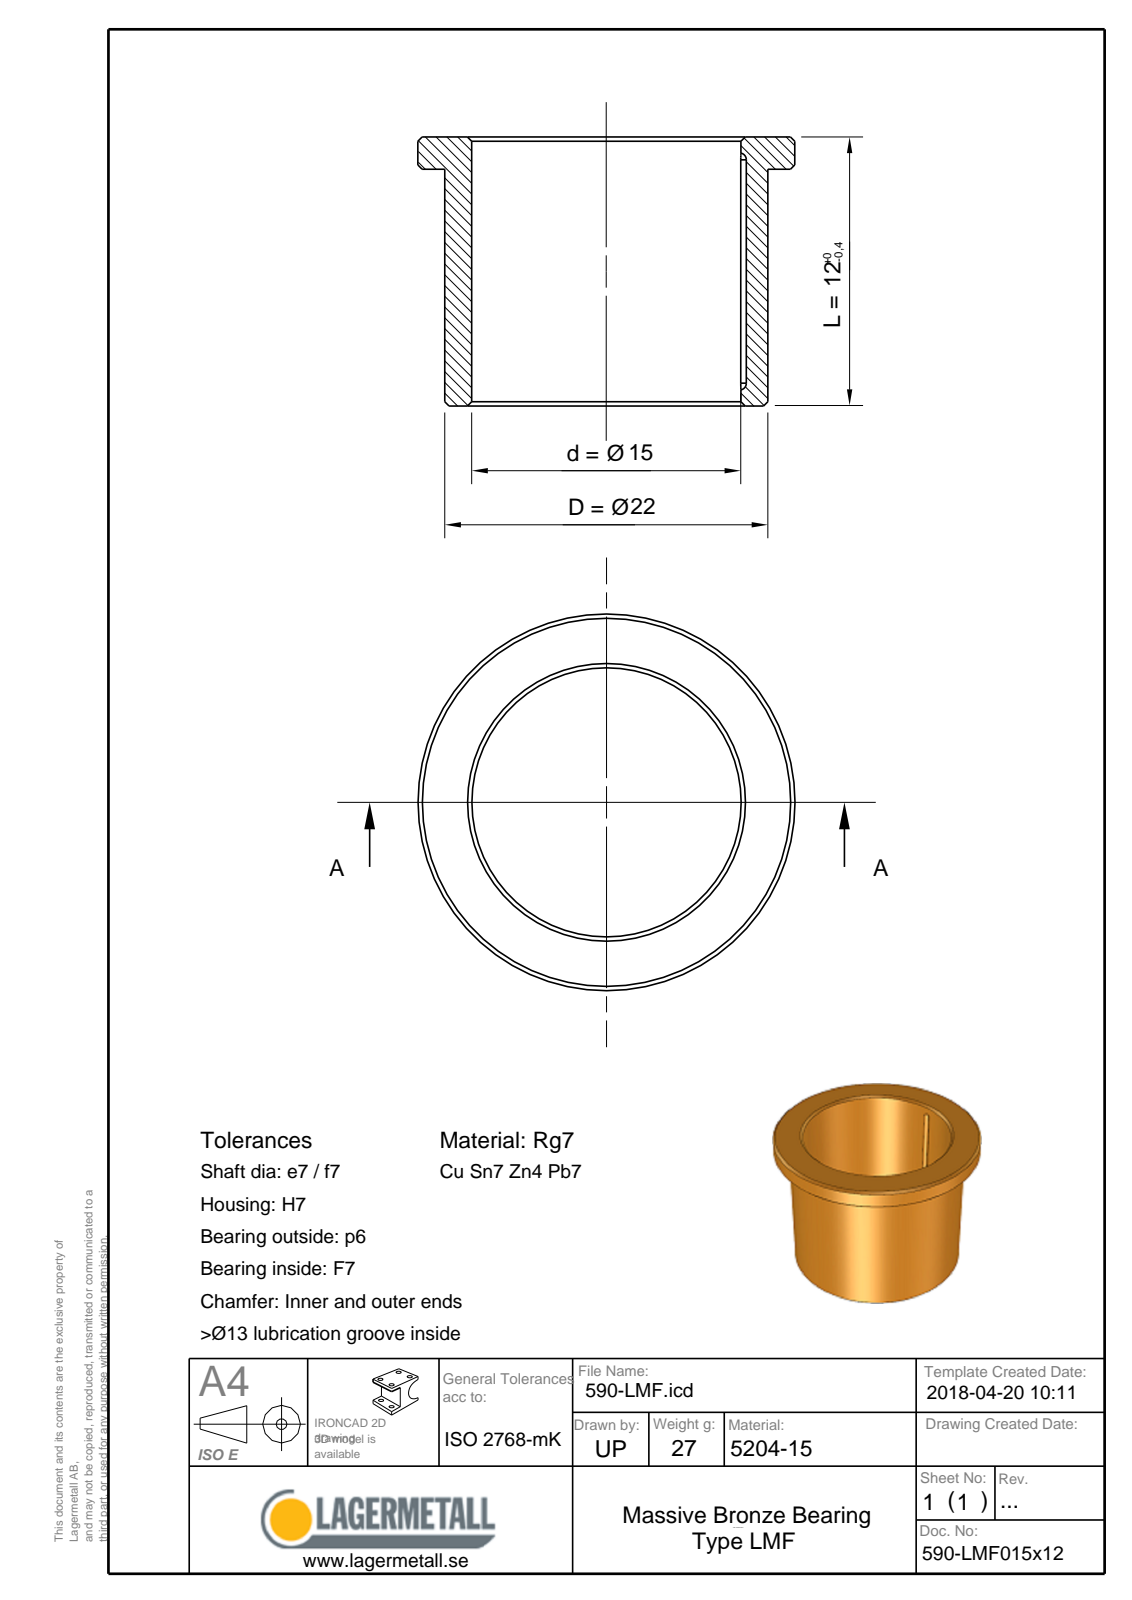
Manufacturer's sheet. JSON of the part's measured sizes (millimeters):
{"part_name": "590-LMF015x12", "step_written_by": "Spatial InterOp 3D (CONFIG_CONTROL_DESIGN)", "units": "millimeters", "bodies": {"solids": 1, "faces": 18, "planar": 5, "cylindrical": 6, "other": 7}, "overall_size": [28, 28, 12], "volume_mm3": 3099, "surface_area_mm2": 2239, "round_holes": [[15, 1]], "round_bosses_or_shafts": [[28, 1], [22, 1]], "partial_cylinders_radius": [[0.75, 3]], "face_to_face_distances": [3, 9, 12, 1.5]}
